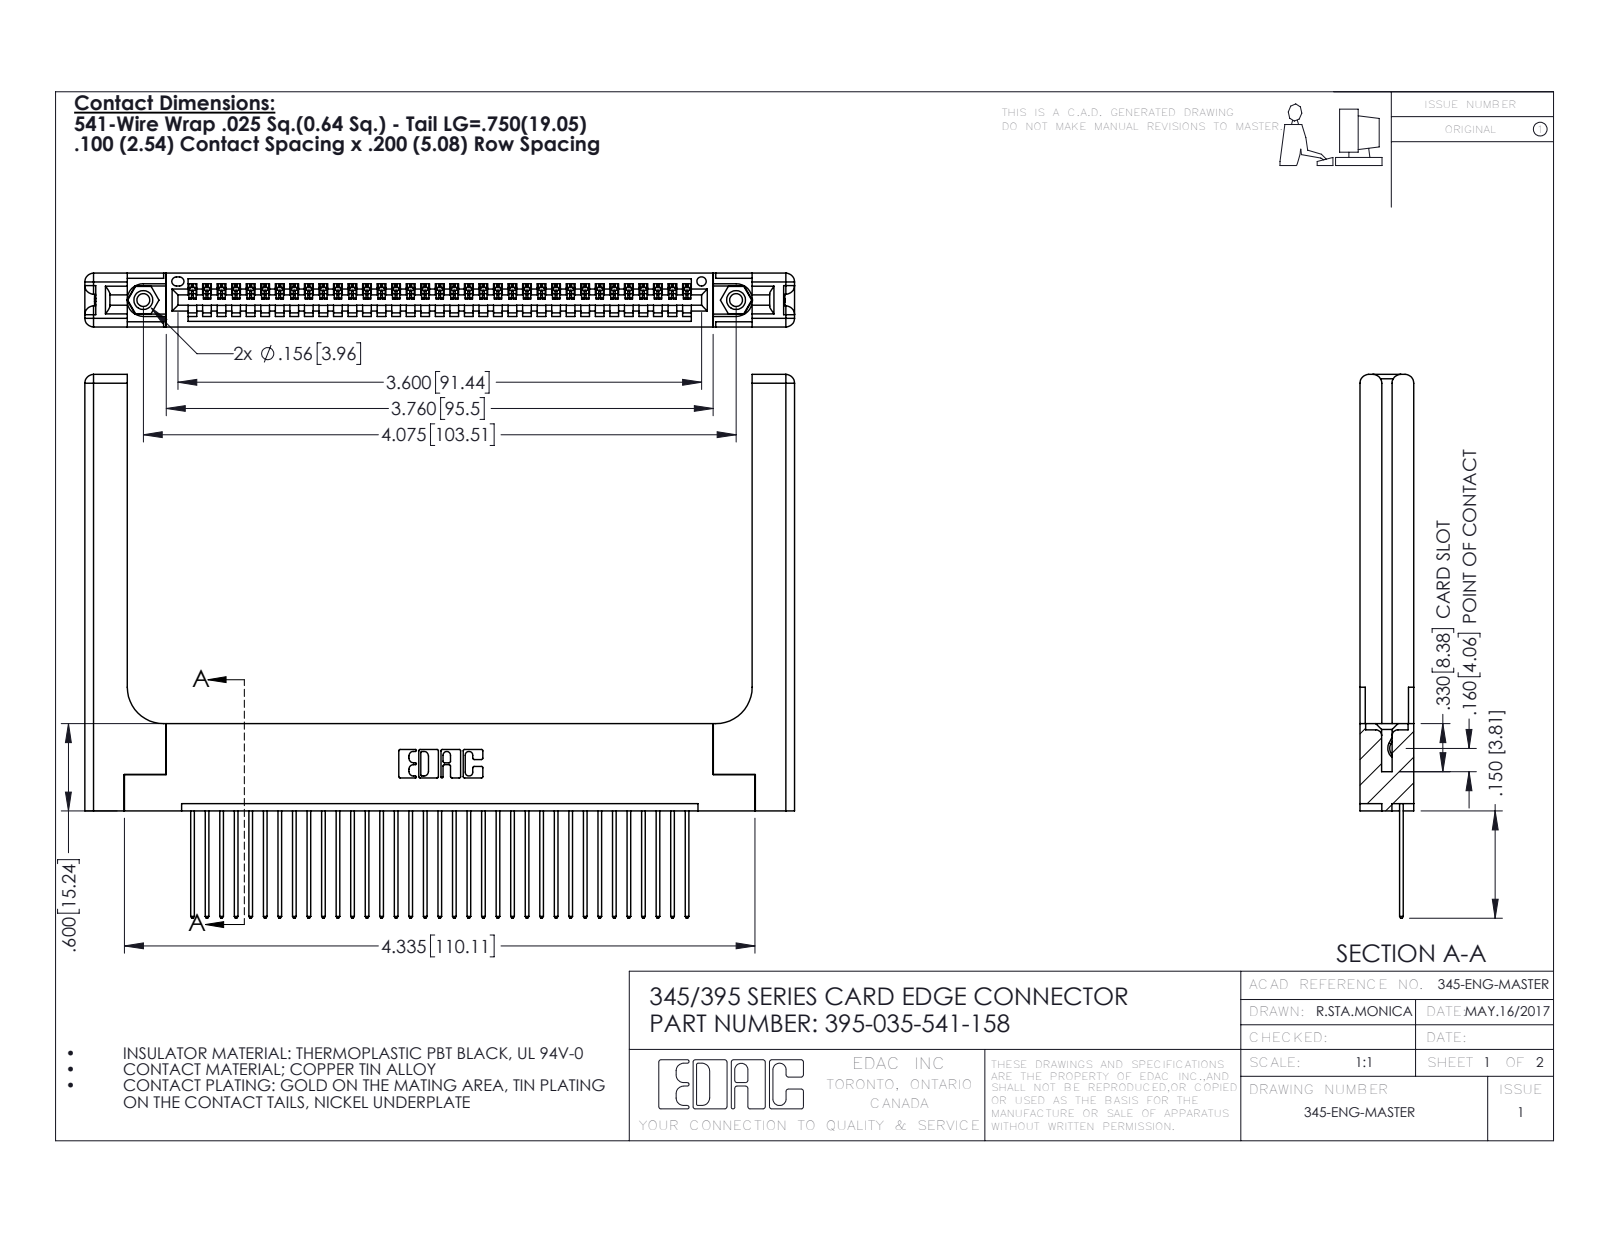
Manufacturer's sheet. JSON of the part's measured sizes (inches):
{"part_name": "345 Part_Flush Mounting Lugs - 0.156 Dia-TH; 395-035-541-158; 345-220-058_345-220-058; 345-250-001_345-250-001-102 (+1 more)", "step_written_by": "SolidWorks 2016 (CONFIG_CONTROL_DESIGN)", "units": "inches", "bodies": {"solids": 40, "faces": 2412, "planar": 1628, "cylindrical": 724, "other": 60}, "overall_size": [4.879, 3.737, 0.37], "volume_in3": 1.241, "surface_area_in2": 33.49, "round_holes": [[0.089, 2], [0.125, 2], [0.156, 2], [0.064, 1]], "round_bosses_or_shafts": [[0.155, 2]], "partial_cylinders_radius": [[0.006, 70], [0.01, 70], [0.01, 22], [0.06, 16], [0.007, 6], [0.031, 6], [0.026, 3], [0.03, 2]], "face_to_face_distances": [0.072, 0.37, 0.298, 0.098, 0.272, 0.025, 0.2, 0.148, 0.15, 0.225], "hole_center_spacings": [0.27, 3.839, 4.075]}
